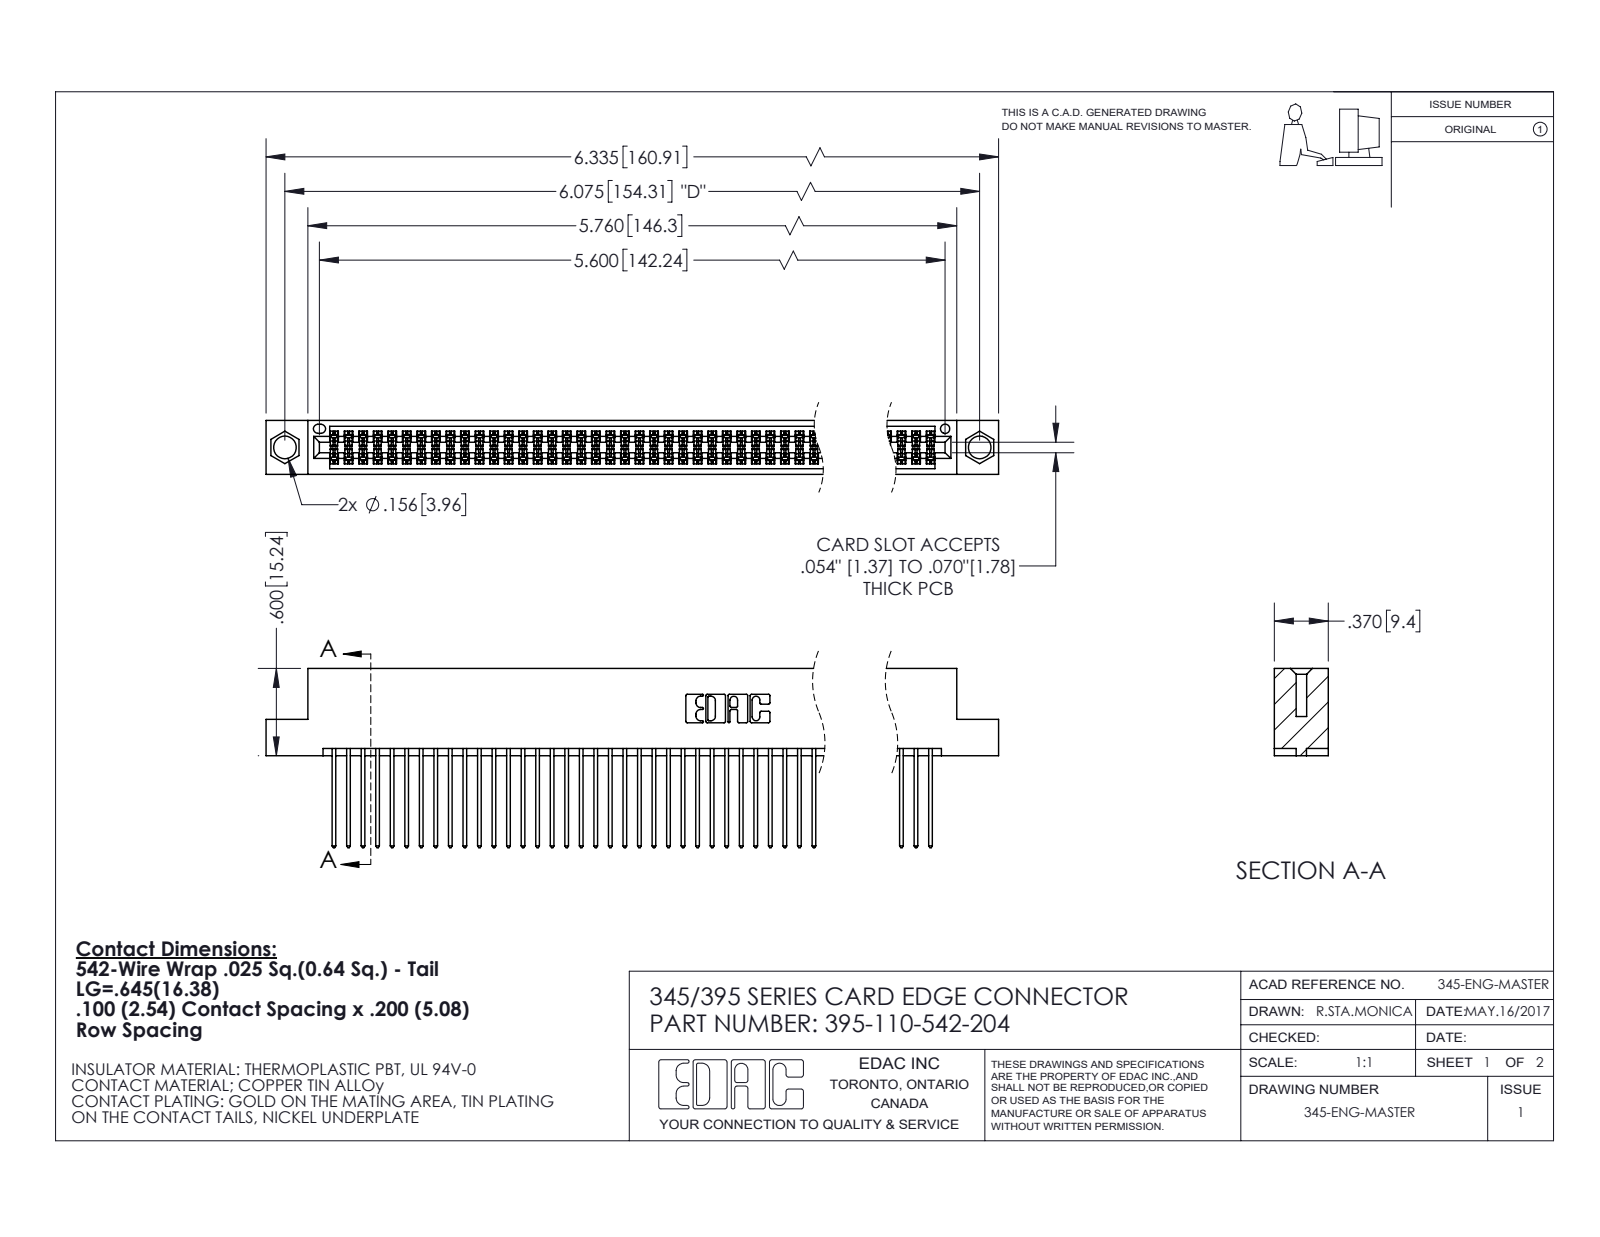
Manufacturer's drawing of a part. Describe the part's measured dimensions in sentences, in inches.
The part is named "345-292-001_345-293-142; 345 Part_Flush Mounting Lugs - 0.156 Dia-TI; 395-110-542-204". Its 3-D file was written by "SolidWorks 2020 (CONFIG_CONTROL_DESIGN)". It is 111 solids with 5640 faces: 3724 planar, 1916 cylindrical and 0 other. Overall it measures 6.335 by 1.232 by 0.37 inches. Its volume is 0.986 cubic inches and its surface area 40.9 square inches. Round holes: 2 of diameter 0.156, 1 of diameter 0.064. Partial cylindrical surfaces (rounded edges, fillets, slot ends): 220 of radius 0.006, 110 of radius 0.01, 22 of radius 0.01, 6 of radius 0.007, 6 of radius 0.031, 3 of radius 0.026, 2 of radius 0.014, 2 of radius 0.019. The main face-to-face distances are 0.298, 0.072, 0.2, 0.098, 0.272, 0.025, 0.225, 0.37, 0.175, 0.149. The hole center spacings are 0.27, 5.839, 6.075.
